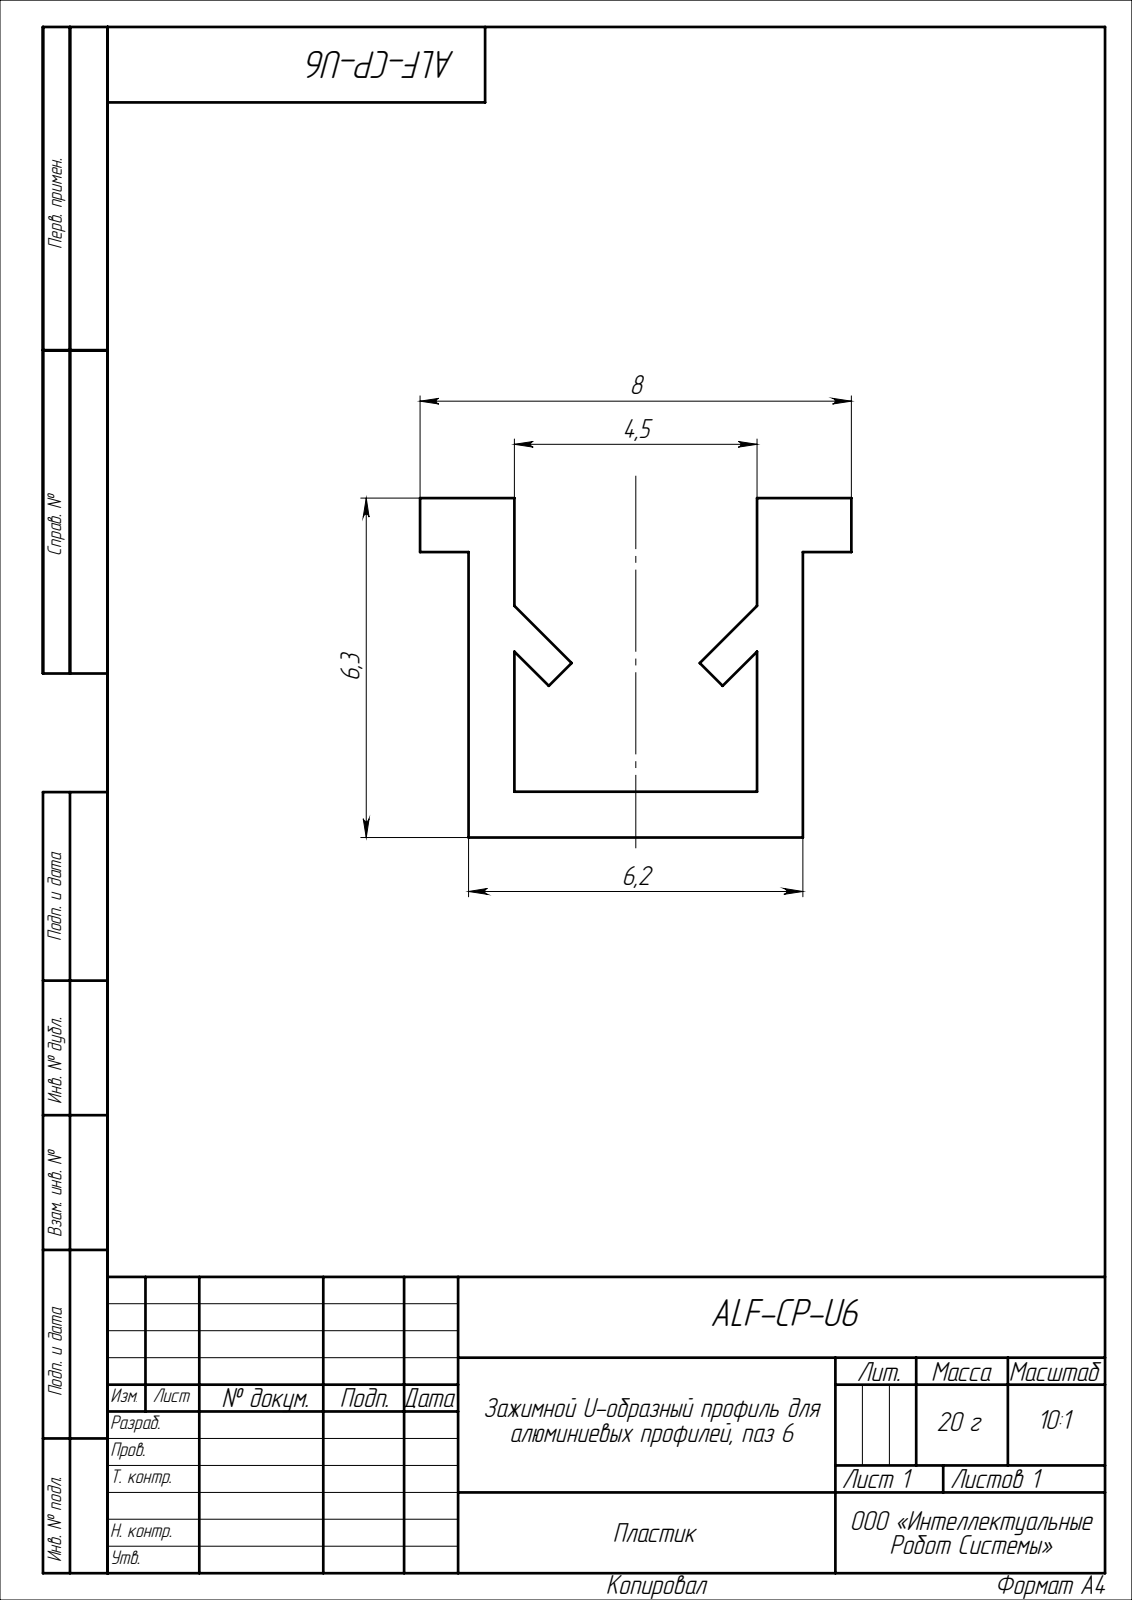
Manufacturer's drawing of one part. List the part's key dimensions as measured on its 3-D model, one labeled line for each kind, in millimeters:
Part name (STEP PRODUCT): ALF-CP-U6
STEP written by: SolidWorks 2022 (CONFIG_CONTROL_DESIGN)
Units: millimetres
Bodies: 1 solid, 22 faces (22 planar, 0 cylindrical, 0 other)
Overall size (bounding box): 1000 × 8 × 6.3
Volume: 17 775 mm³ · Surface area: 43 838 mm²
Main face-to-face distances: 0.85, 5.35, 6.2, 4.5, 6.3, 5.45, 0.9, 1.75, 6.25, 7.1
